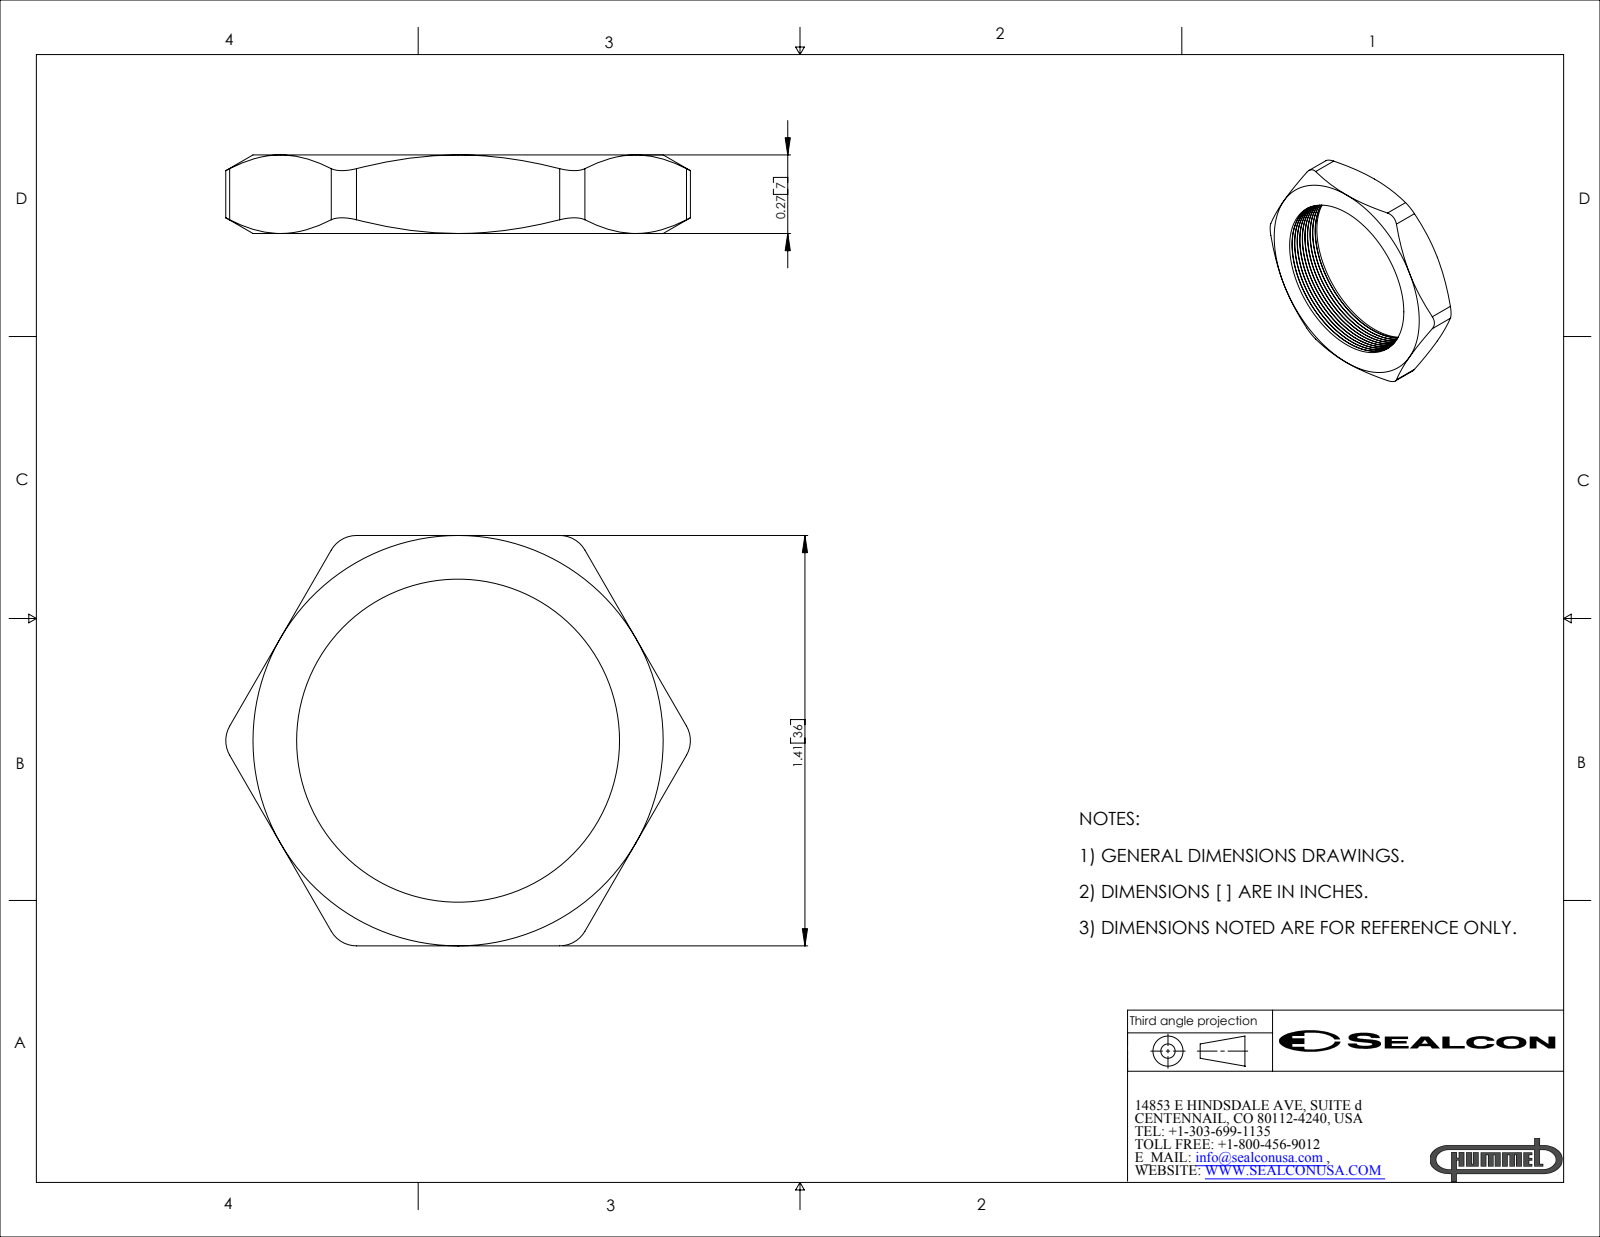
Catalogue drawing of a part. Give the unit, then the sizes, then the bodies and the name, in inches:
Units: inches
Overall size (bounding box): 1.597 × 1.41 × 0.27
Round holes (diameter × count): ⌀1.11 ×1
Partial cylindrical surfaces — rounded edges, fillets, slot ends (radius × count): R0.1 ×6
Main face-to-face distances: 0.27, 1.41
Volume: 0.188 in³ · Surface area: 4.481 in²
Bodies: 1 solid, 93 faces (8 planar, 27 cylindrical, 58 other)
Part name (STEP PRODUCT): NP-21-GY
STEP written by: SolidWorks 2007 (CONFIG_CONTROL_DESIGN)
